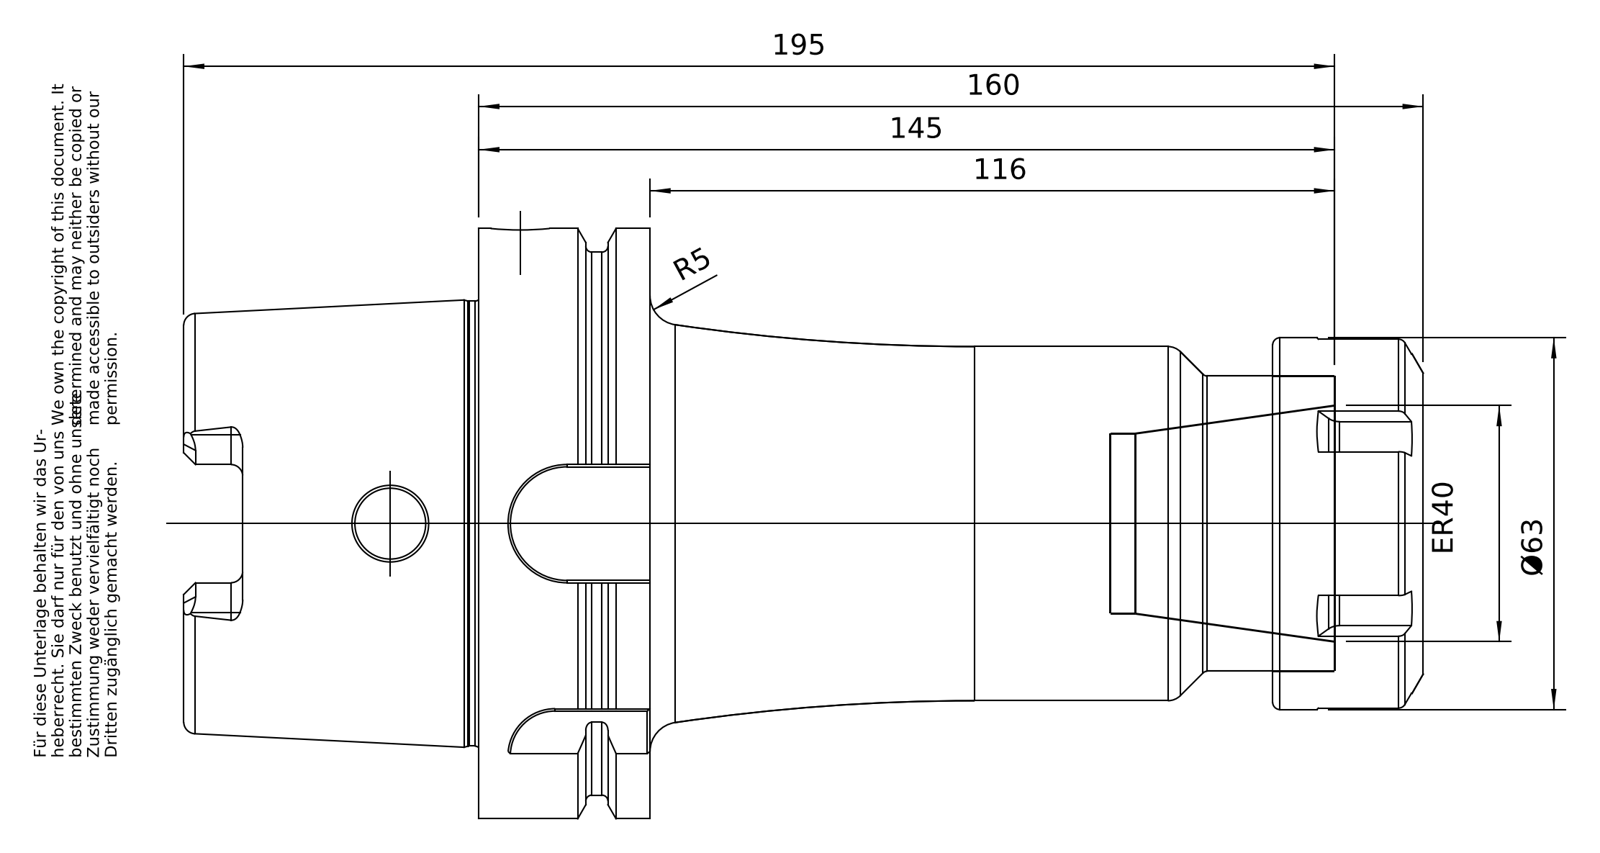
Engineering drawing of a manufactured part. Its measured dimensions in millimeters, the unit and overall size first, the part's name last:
Units: millimetres
Overall size (bounding box): 210 × 100 × 100
Round holes (diameter × count): ⌀10 ×1, ⌀12 ×1, ⌀22.5 ×1, ⌀24 ×1, ⌀24.32 ×1, ⌀24.5 ×1, ⌀30.5 ×1, ⌀53 ×1, ⌀63 ×1
Round bosses / shafts (diameter × count): ⌀100 ×1, ⌀92 ×1, ⌀75.36 ×1, ⌀60 ×1, ⌀50 ×1
Partial cylindrical surfaces — rounded edges, fillets, slot ends (radius × count): R2 ×6, R2.7 ×6, R5 ×4, R8 ×1, R10.02 ×1, R11.02 ×1
Main face-to-face distances: 29, 134.5, 105.5, 160, 131, 25.5, 12.5, 16.5, 122, 147.5
Volume: 616 843 mm³ · Surface area: 84 803 mm²
Bodies: 2 solids, 229 faces (80 planar, 60 cylindrical, 89 other)
Part name (STEP PRODUCT): A100-022-40; 83-912-40; A100-022-40_ASM
STEP written by: PRO/ENGINEER BY PARAMETRIC TECHNOLOGY CORPORATION, 2010430 (CONFIG_CONTROL_DESIGN)
